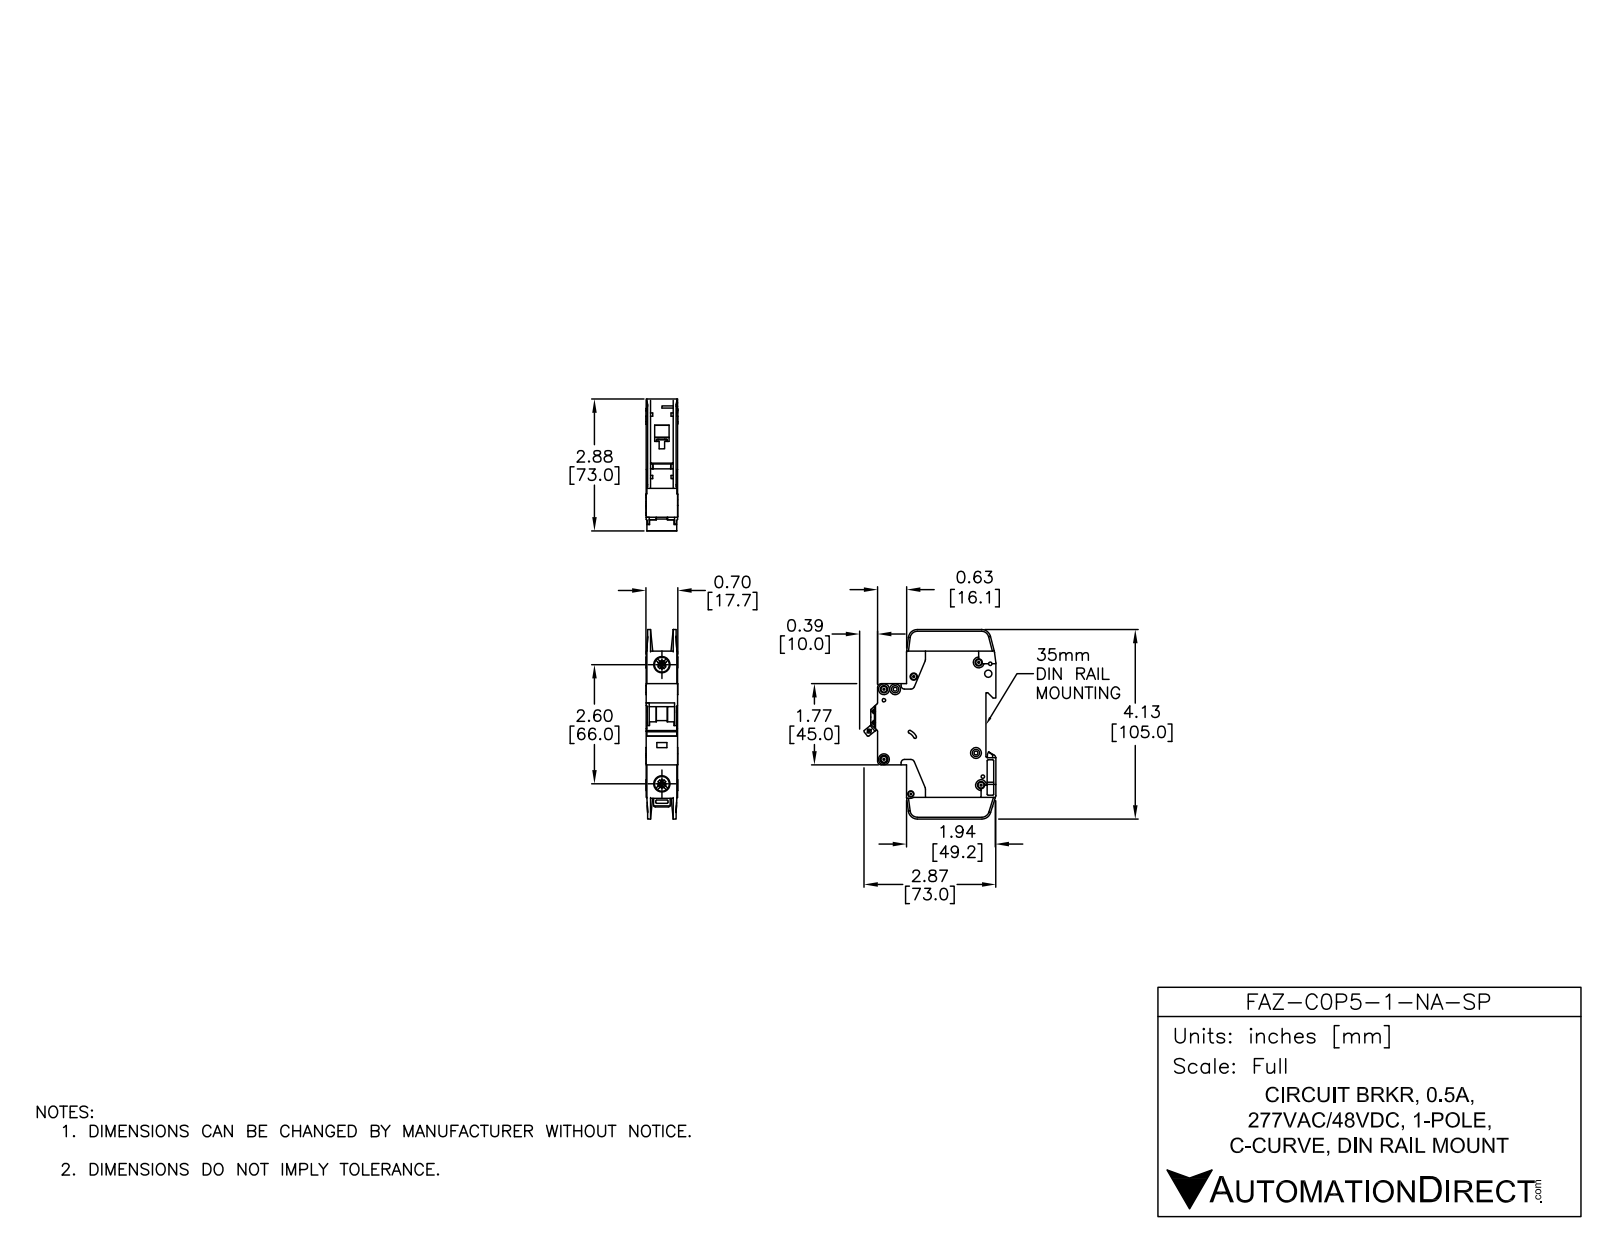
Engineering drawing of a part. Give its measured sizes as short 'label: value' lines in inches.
name: FAZ-C0P5-1-NA-SP
written by: SolidWorks 2014 (AUTOMOTIVE_DESIGN)
unit: in
bodies: 3 solids, 784 faces (409 planar, 263 cylindrical, 112 other)
size: 4.134 × 2.876 × 0.697
volume: 4.741 in³; area: 38.35 in²
holes: 7× ⌀0.142, 2× ⌀0.043, 2× ⌀0.059, 2× ⌀0.157, 2× ⌀0.281, 2× ⌀0.323, 1× ⌀0.075, 1× ⌀0.085, 1× ⌀0.087, 1× ⌀0.1, 1× ⌀0.13, 1× ⌀0.134
bosses: 7× ⌀0.236, 1× ⌀0.098
rounds: 29× R0.01, 18× R0.02, 10× R0.039, 10× R0.079, 5× R0.197, 4× R0.157, 3× R0.071, 2× R0.008
face distances: 0.689, 0.593, 0.028, 0.096, 0.069, 0.62, 0.524, 0.551, 0.496, 0.079
hole spacings: 0.244, 0.204, 0.24, 0.322, 0.337, 0.343, 0.437, 0.49
